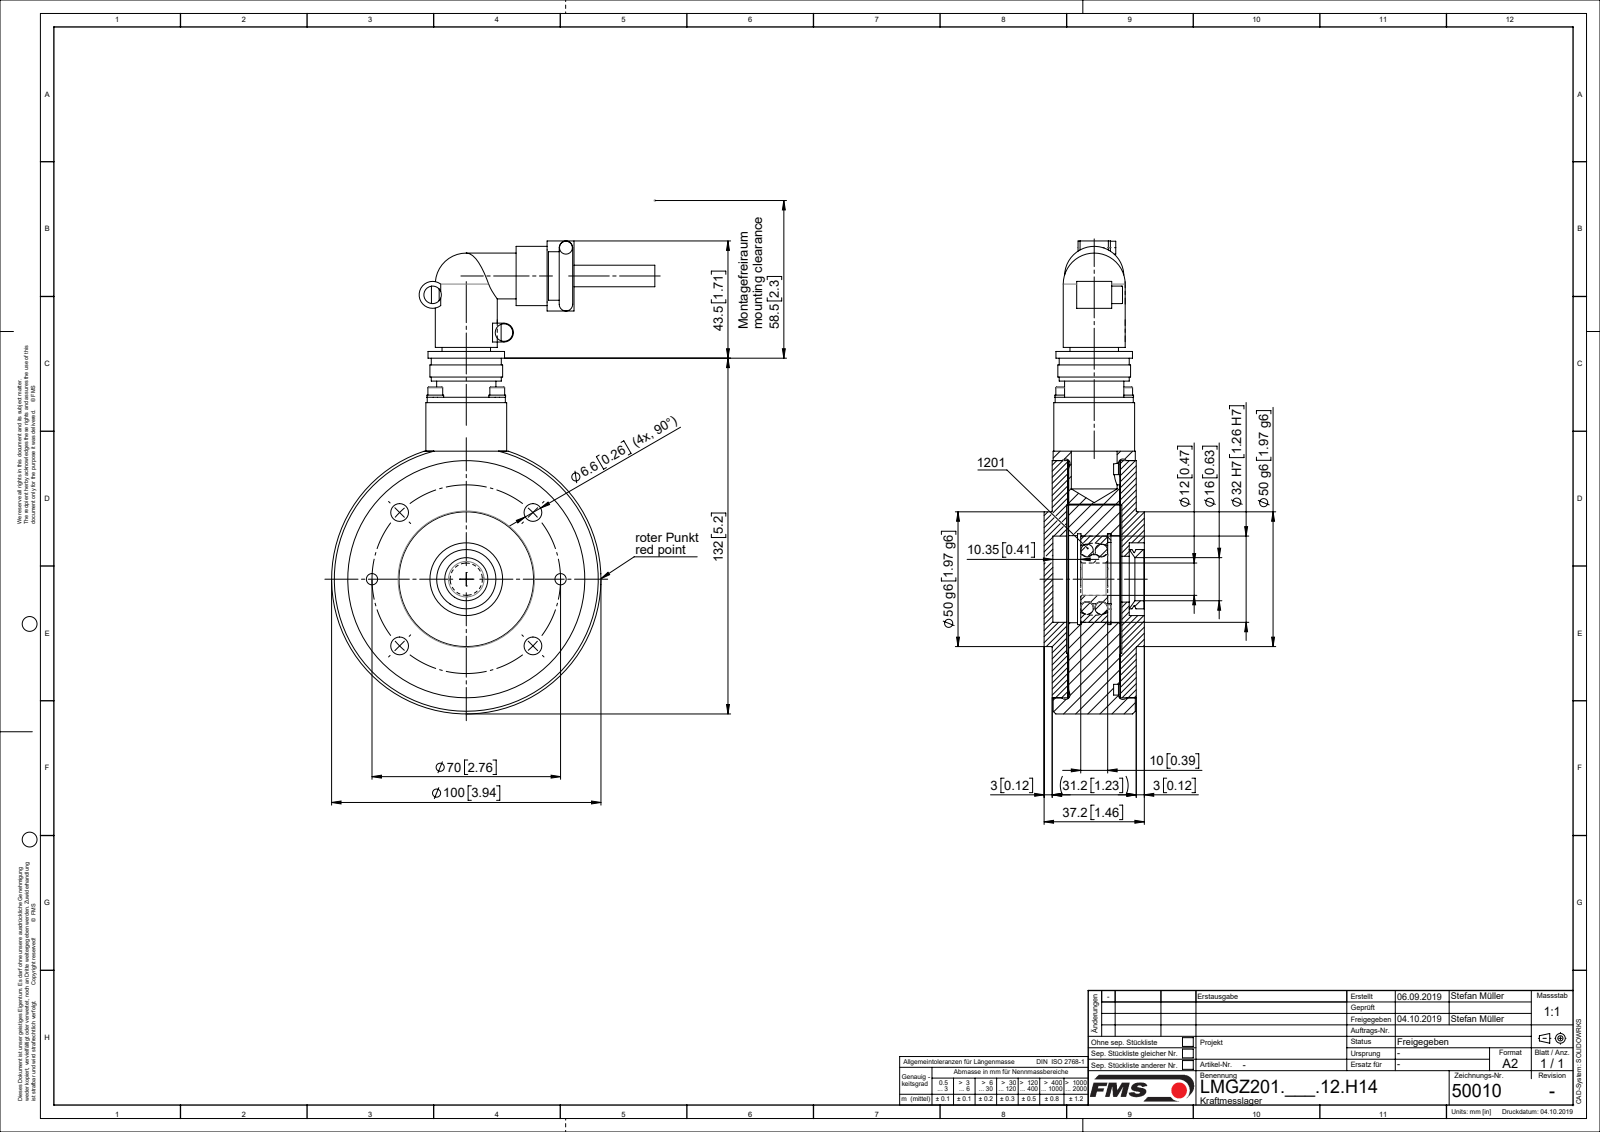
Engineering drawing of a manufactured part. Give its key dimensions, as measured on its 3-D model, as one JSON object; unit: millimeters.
{"part_name": "L50010; L4866604; TEIL1; L48891 (+8 more)", "step_written_by": "Mechanical Desktop 2007 (CONFIG_CONTROL_DESIGN)", "units": "millimeters", "bodies": {"solids": 20, "faces": 385, "planar": 123, "cylindrical": 221, "other": 41}, "overall_size": [175.5, 120, 37.2], "volume_mm3": 274467, "surface_area_mm2": 98513, "round_holes": [[2.6, 4], [3.2, 4], [3.4, 4], [3.5, 4], [6.6, 4], [4, 2], [5.5, 2], [10, 2], [12, 1], [16, 1], [17, 1], [23, 1]], "round_bosses_or_shafts": [[6.2, 4], [5.5, 4], [3, 4], [22, 3], [8, 3], [6.5, 2], [5, 2], [4.8, 2]], "partial_cylinders_radius": [[2.5, 2], [3.5, 1], [5, 1]], "face_to_face_distances": [19.25, 19, 5.85, 25.1, 6.1, 25.35, 19.5, 5.5, 24.75, 20], "hole_center_spacings": [35, 16.26, 23, 26.79, 49.5, 64.67, 70, 32.53]}
